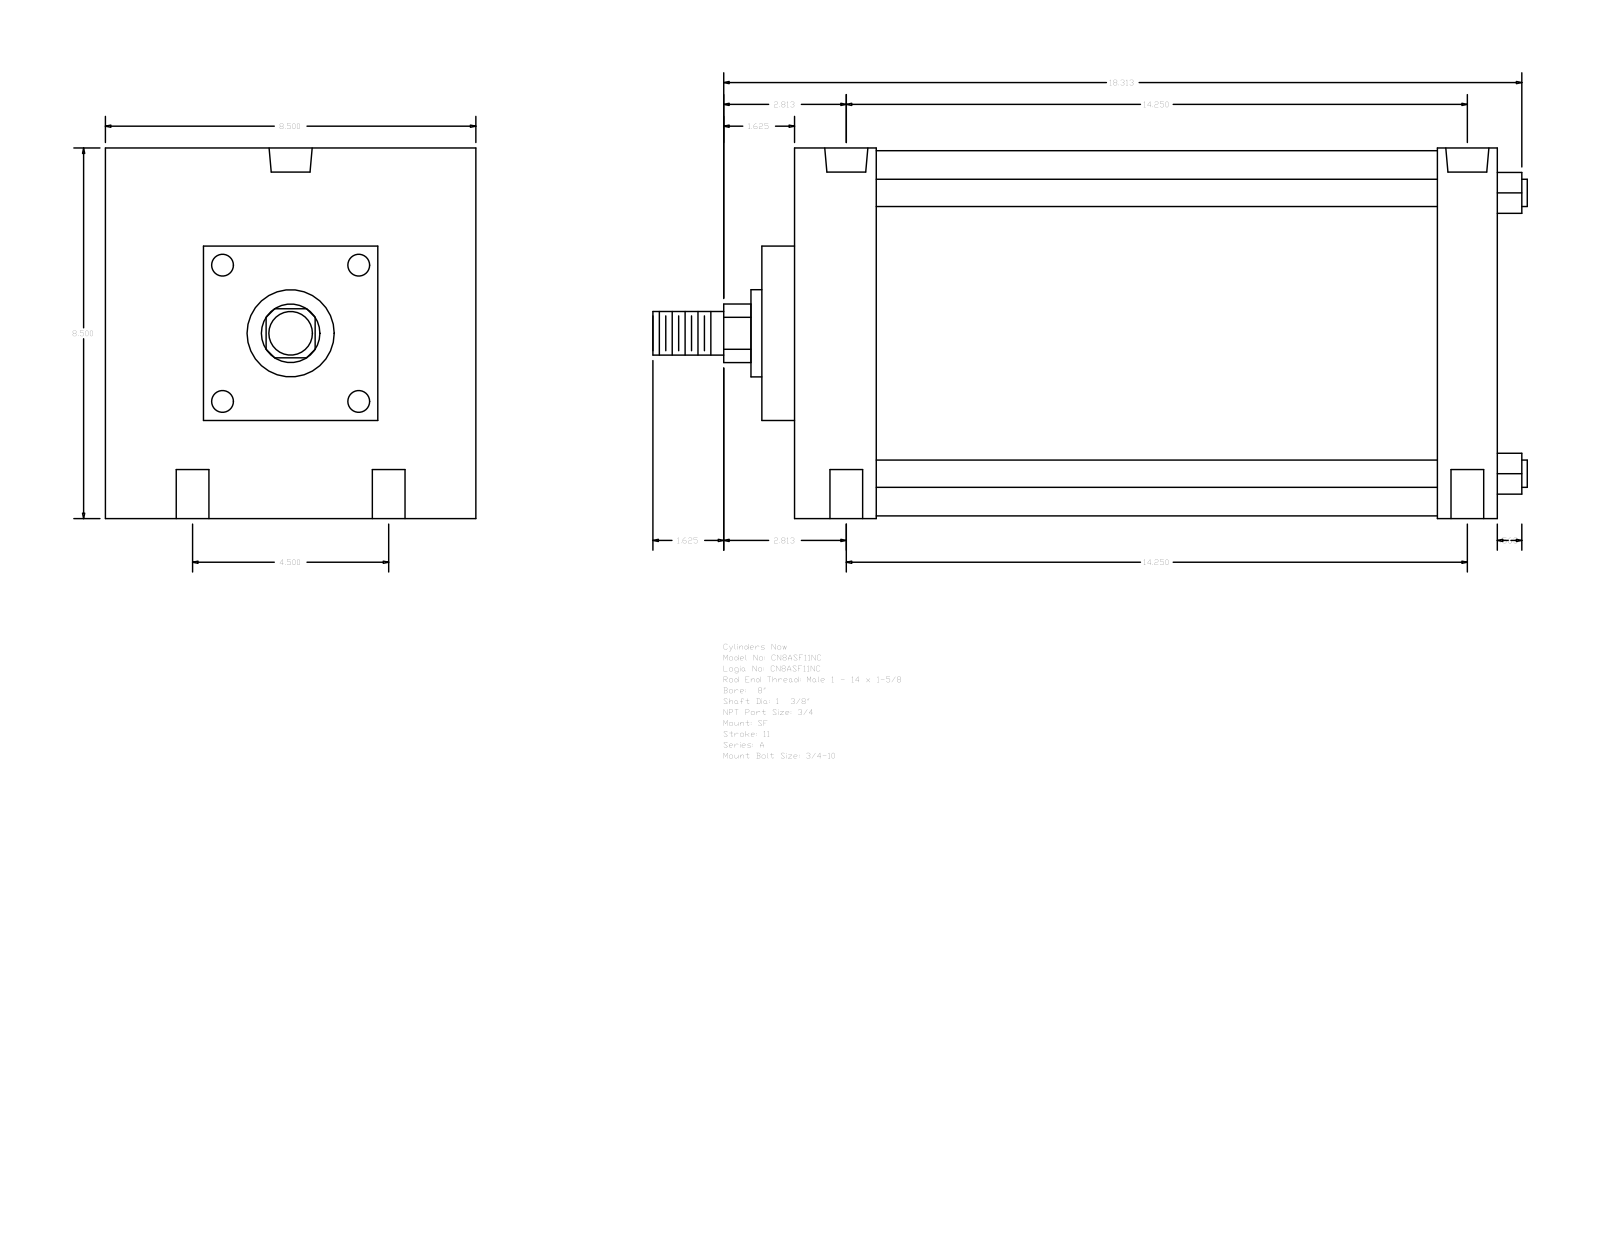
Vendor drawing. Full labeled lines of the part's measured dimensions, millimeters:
Part name (STEP PRODUCT): A_SF__0800_1.375
STEP written by: GSSL Pune (CONFIG_CONTROL_DESIGN)
Units: millimetres
Bodies: 0 solids, 93 faces (67 planar, 26 cylindrical, 0 other)
Overall size (bounding box): 509.59 × 215.9 × 215.9
Round holes (diameter × count): ⌀19.05 ×4, ⌀15.08 ×2, ⌀25.12 ×2
Round bosses / shafts (diameter × count): ⌀15.88 ×4, ⌀212.72 ×1, ⌀50.8 ×1, ⌀34.92 ×1, ⌀25.4 ×1
Partial cylindrical surfaces — rounded edges, fillets, slot ends (radius × count): R17.06 ×1
Main face-to-face distances: 409.58, 215.9, 47.63, 374.66, 327.03, 361.95, 34.92, 19.04, 66.67, 393.7
Hole centre spacings: 57.15, 366.43, 361.95, 114.3, 379.57, 349.25
